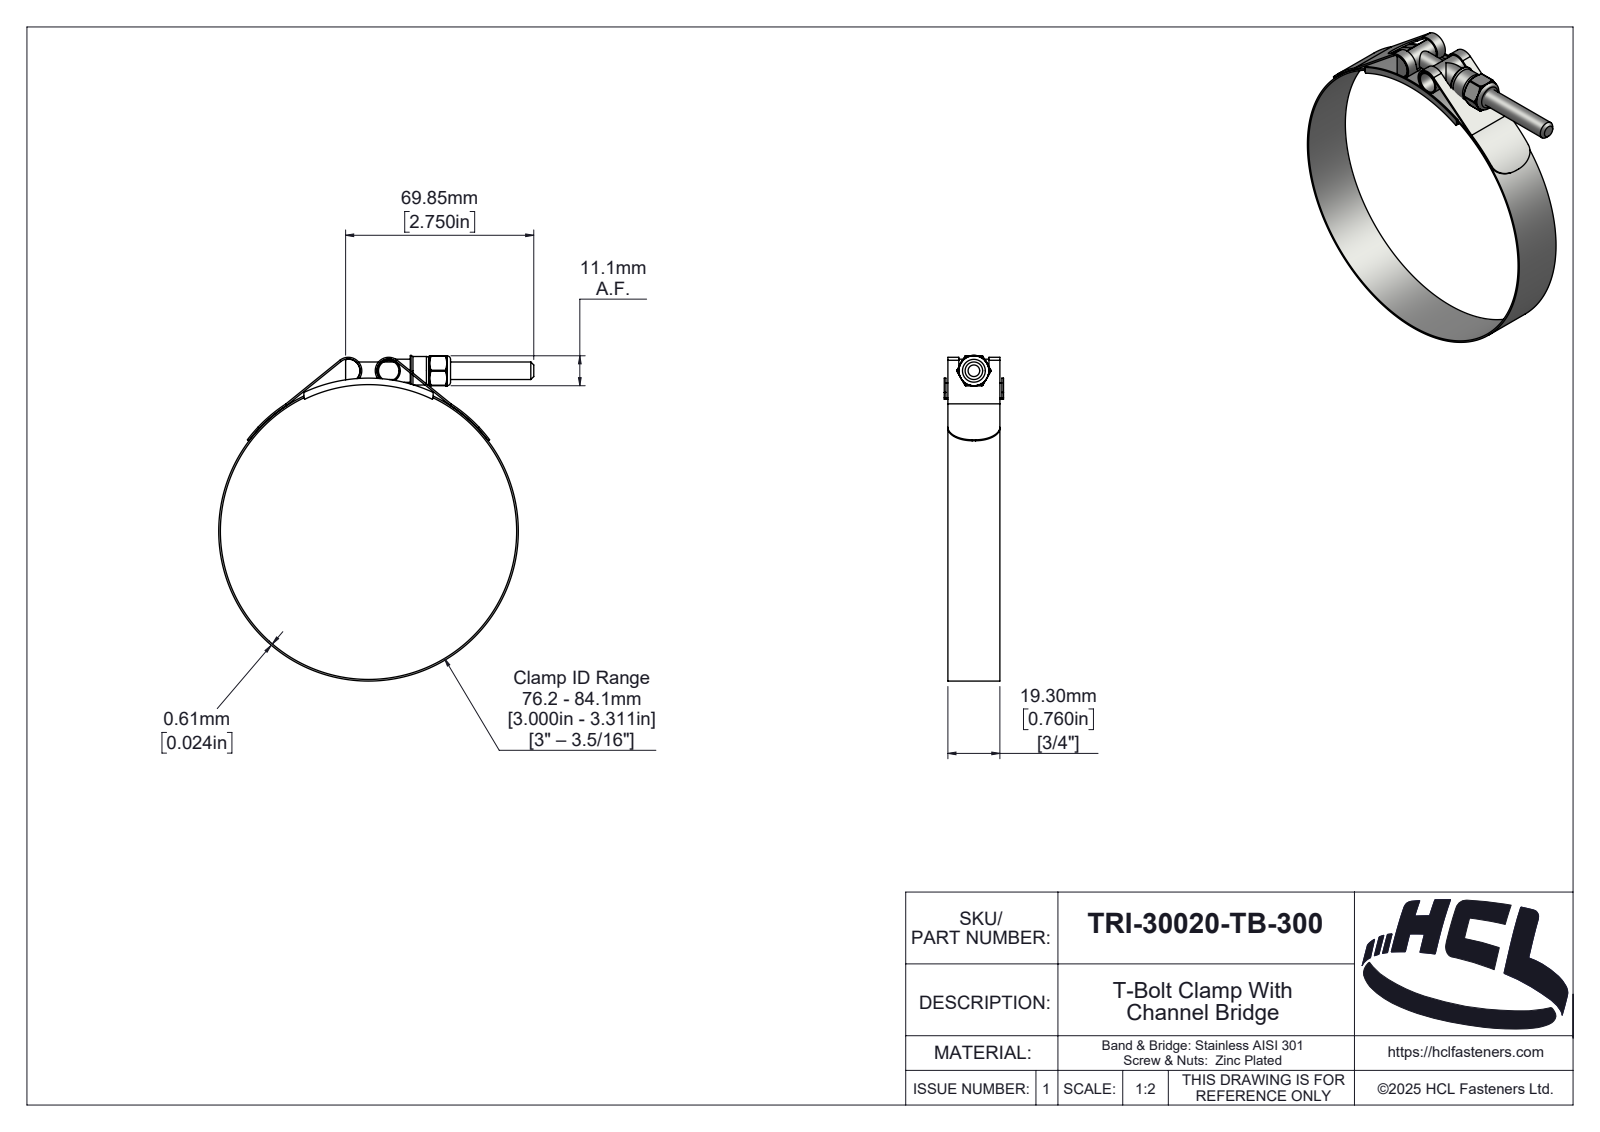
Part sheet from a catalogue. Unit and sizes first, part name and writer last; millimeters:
Units: millimetres
Overall size (bounding box): 120.86 × 116.96 × 22
Round holes (diameter × count): ⌀5.4 ×1, ⌀6.35 ×1, ⌀6.5 ×1, ⌀7.58 ×1, ⌀110 ×1
Round bosses / shafts (diameter × count): ⌀8.58 ×2, ⌀111.22 ×1, ⌀10.58 ×1
Partial cylindrical surfaces — rounded edges, fillets, slot ends (radius × count): R0.39 ×6, R0.5 ×2, R4.39 ×2, R5 ×2, R0.59 ×1, R2.42 ×1, R3.03 ×1, R3.19 ×1
Main face-to-face distances: 0.61, 19.3, 1.35, 20.65, 0.74, 21.39, 20.04, 22, 20.78, 31
Hole centre spacings: 60
Volume: 9 971 mm³ · Surface area: 24 058 mm²
Bodies: 6 solids, 330 faces (44 planar, 122 cylindrical, 164 other)
Part name (STEP PRODUCT): TRI-30020-TB-300
STEP written by: SolidWorks 2025 (AUTOMOTIVE_DESIGN)
